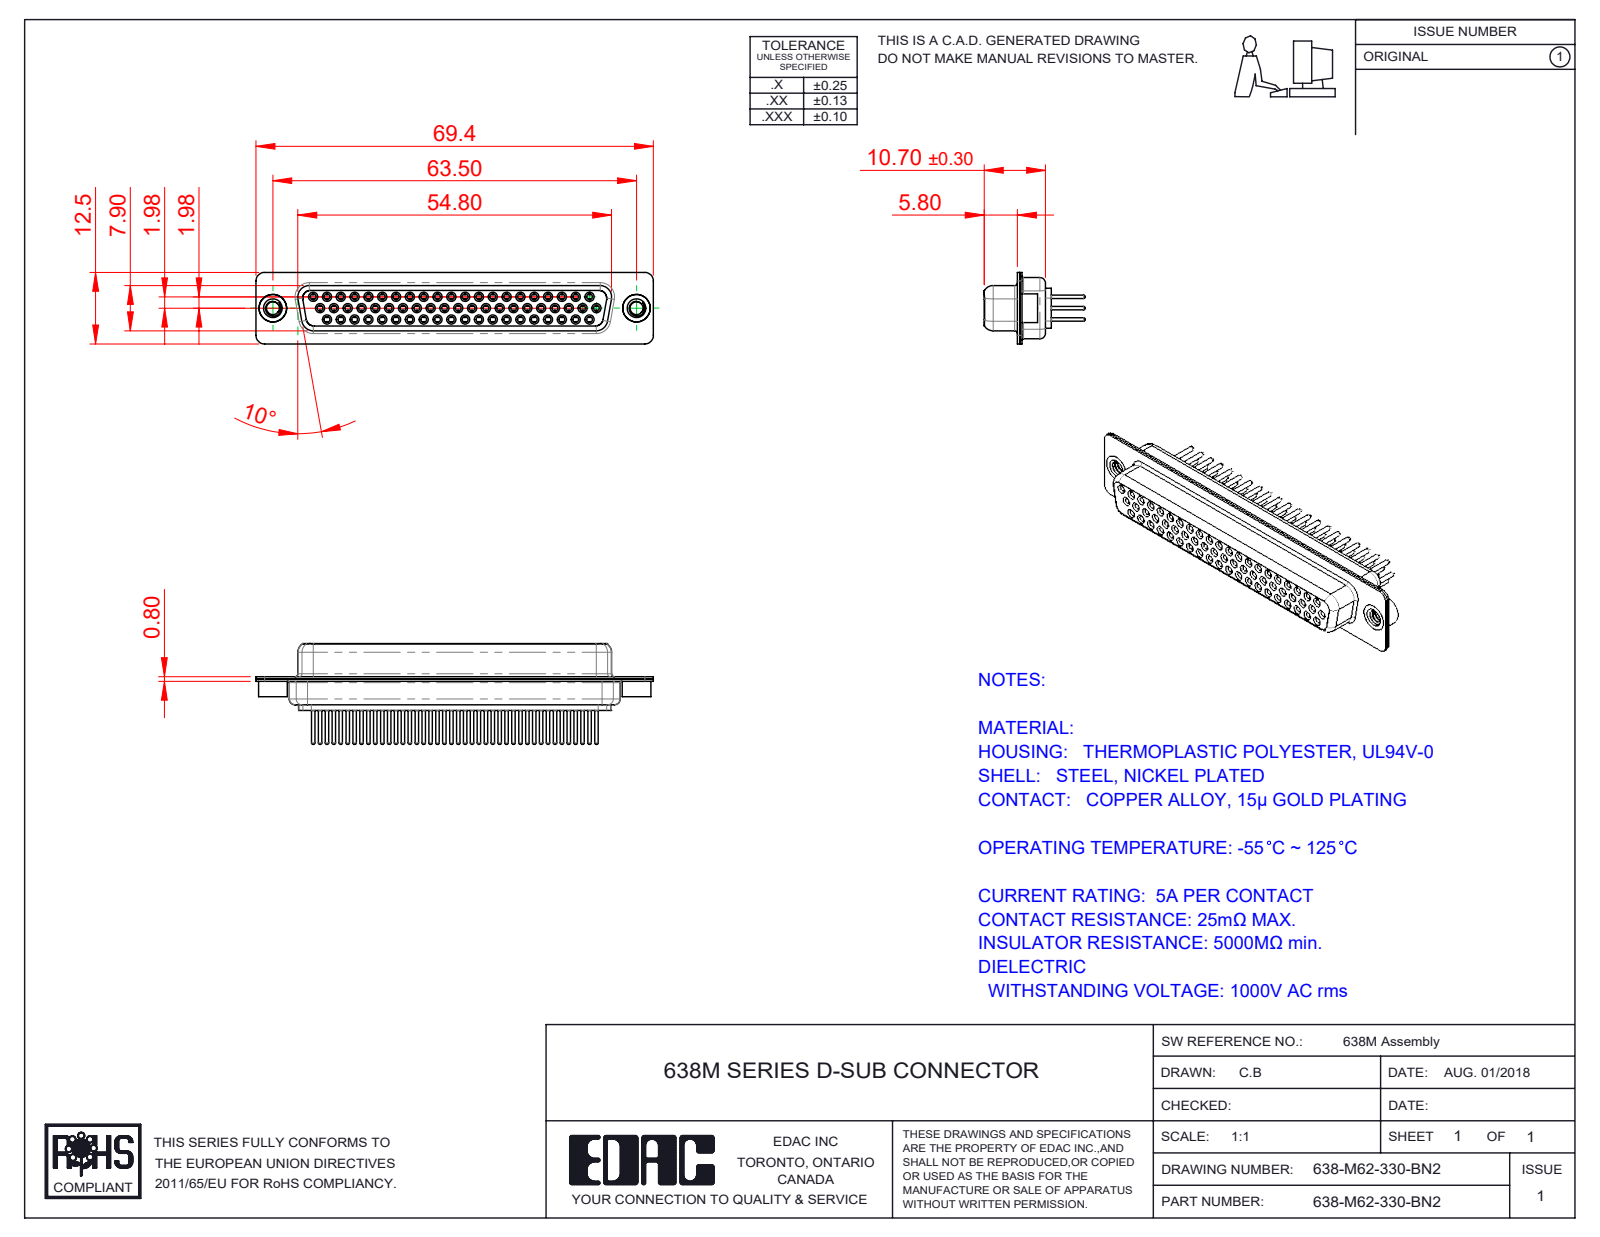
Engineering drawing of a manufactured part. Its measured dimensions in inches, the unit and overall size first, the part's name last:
Units: inches
Overall size (bounding box): 2.732 × 0.693 × 0.492
Round holes (diameter × count): ⌀0.039 ×62, ⌀0.043 ×62, ⌀0.067 ×62, ⌀0.071 ×62, ⌀0.079 ×62, ⌀0.089 ×2, ⌀0.157 ×2, ⌀0.189 ×2
Round bosses / shafts (diameter × count): ⌀0.087 ×62, ⌀0.063 ×62, ⌀0.059 ×62, ⌀0.024 ×62, ⌀0.197 ×2, ⌀0.193 ×2
Partial cylindrical surfaces — rounded edges, fillets, slot ends (radius × count): R0.059 ×16, R0.079 ×12, R0.053 ×8, R0.063 ×8, R0.01 ×4, R0.02 ×4, R0.024 ×4, R0.026 ×4
Main face-to-face distances: 0.016, 0.055, 0.018, 0.333, 0.35, 0.039, 0.071, 0.244, 0.278, 0.073
Hole centre spacings: 0.285, 0.091, 0.095, 0.163, 0.38, 0.19, 0.57, 0.665
Volume: 0.304 in³ · Surface area: 25.48 in²
Bodies: 67 solids, 3689 faces (997 planar, 1315 cylindrical, 1377 other)
Part name (STEP PRODUCT): 638M Contact Row 1_30; 638M Housing_62 Contacts; 638M Shell Rear_62 Contacts; 638M Shell Front_62 Contacts (+4 more)
STEP written by: SolidWorks 2020 (CONFIG_CONTROL_DESIGN)
